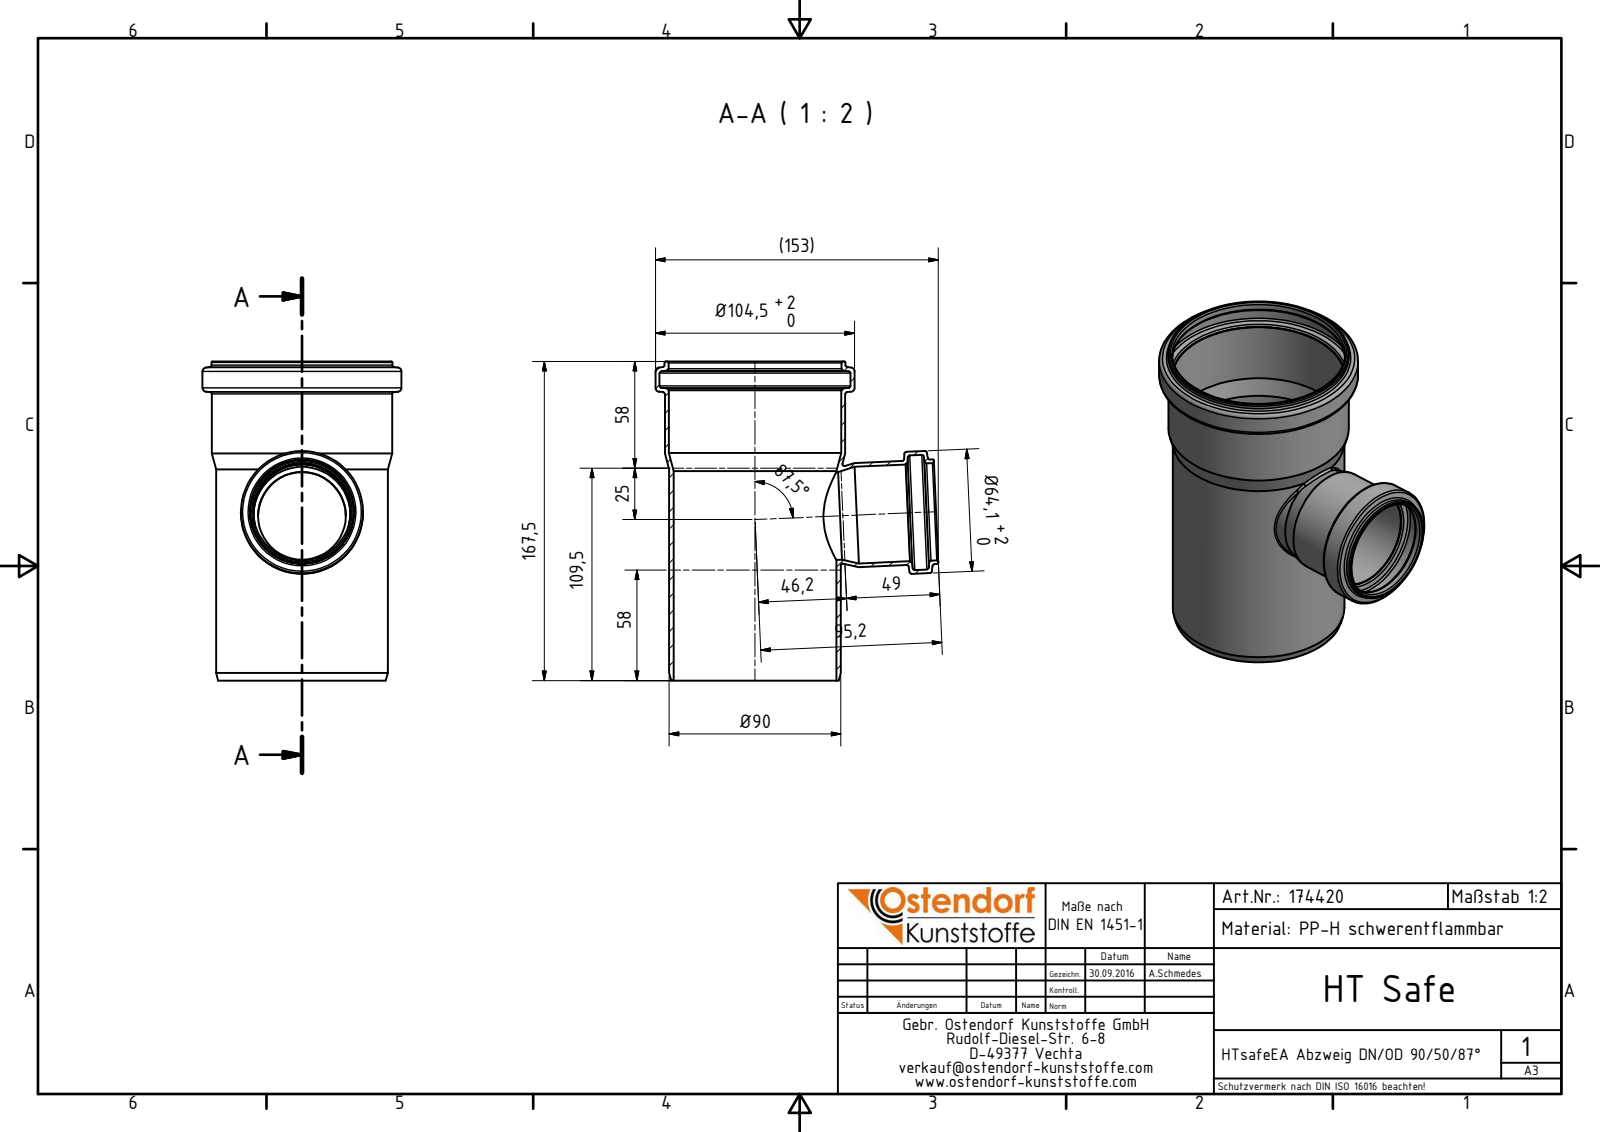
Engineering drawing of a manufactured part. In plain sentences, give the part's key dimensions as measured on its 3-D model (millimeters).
The part is named "174420 HTsafeEA DN_OD 90_50_87°". Its 3-D file was written by "Autodesk Inventor 2016 (AUTOMOTIVE_DESIGN)". It is 1 solid with 61 faces: 5 planar, 19 cylindrical and 37 other. Overall it measures 167.5 by 148.53 by 104.5 millimeters. Its volume is 129 353 cubic millimeters and its surface area 117 494 square millimeters. Round holes: 2 of diameter 51.1, 1 of diameter 46.1, 1 of diameter 50.8, 1 of diameter 60.3, 1 of diameter 85.4, 1 of diameter 90.5, 1 of diameter 90.8, 1 of diameter 100.3. Round bosses or shafts: 1 of diameter 104.5, 1 of diameter 95, 1 of diameter 94.7, 1 of diameter 90.2, 1 of diameter 64.1, 1 of diameter 54.9, 1 of diameter 54.6. Partial cylindrical surfaces (rounded edges, fillets, slot ends): 1 of radius 25.05. The main face-to-face distances are 167.5, 152.29, 15.21, 14.9.
